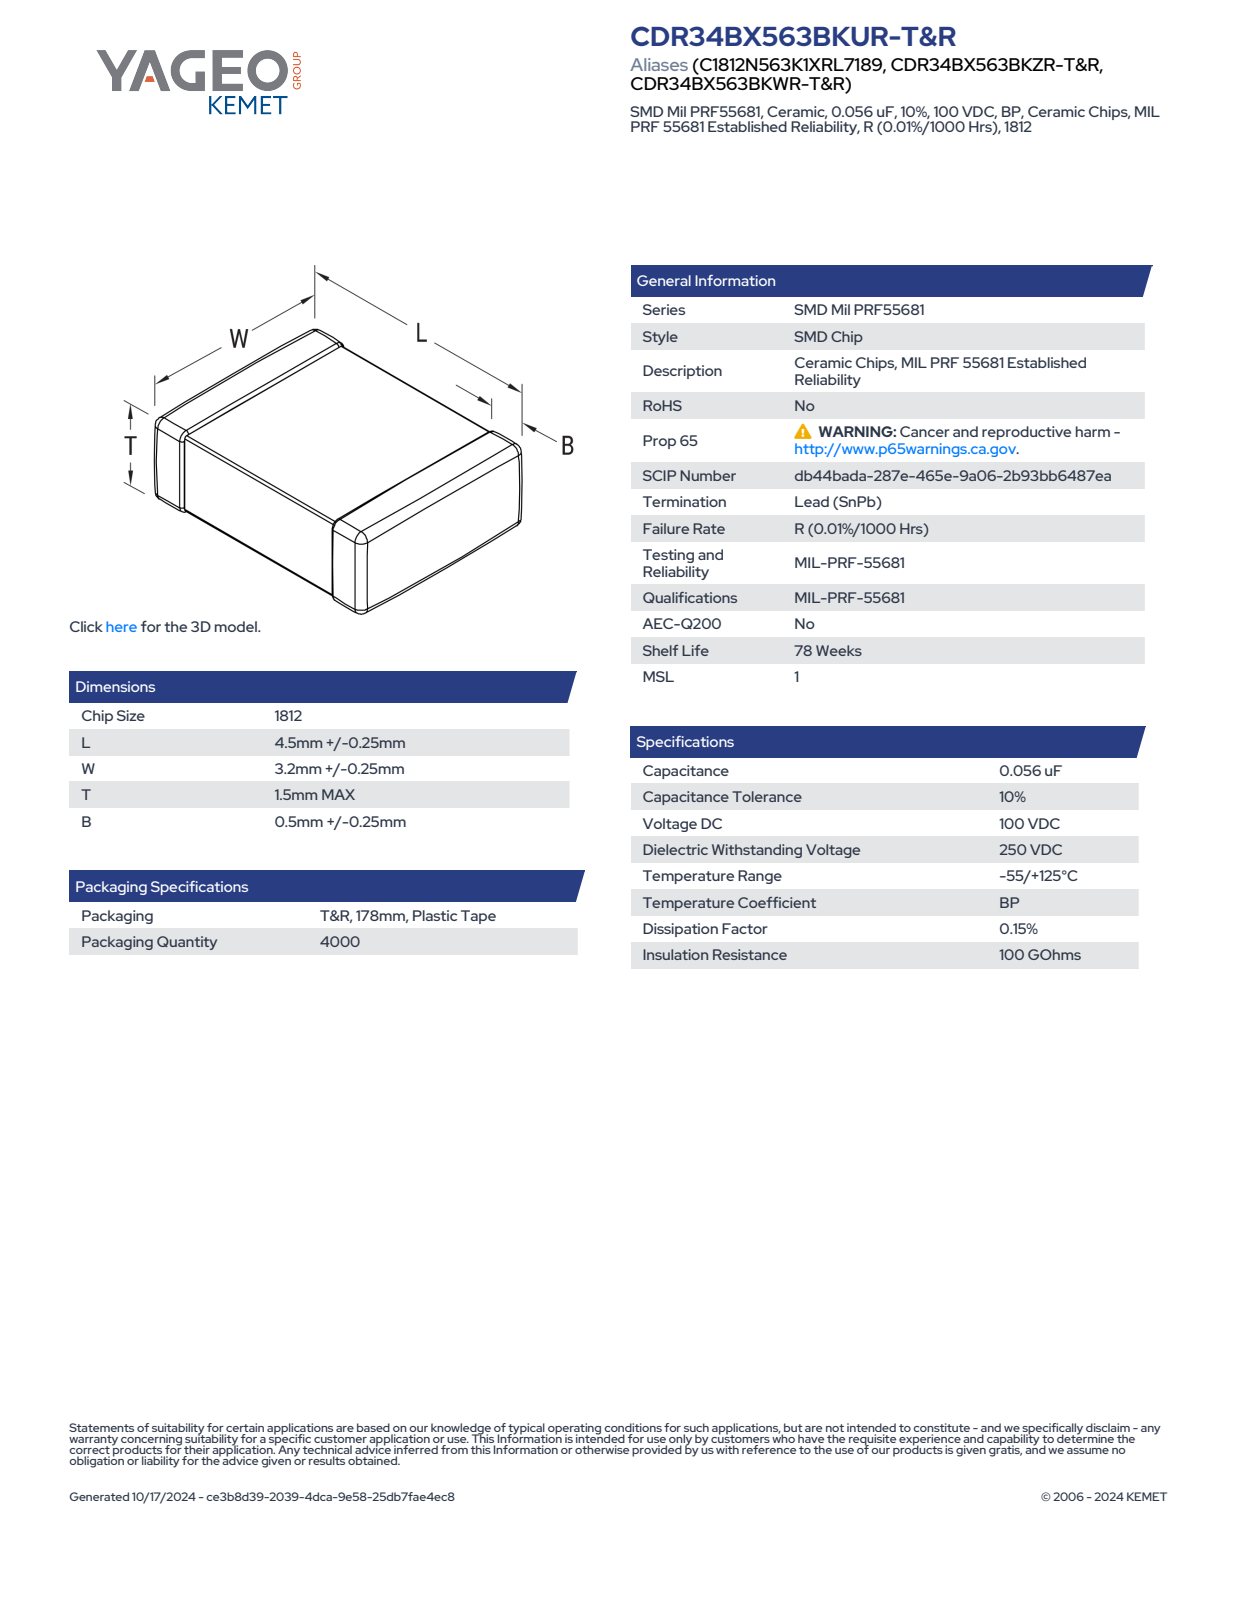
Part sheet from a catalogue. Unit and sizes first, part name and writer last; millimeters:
Units: millimetres
Overall size (bounding box): 4.75 × 3.45 × 1.5
Main face-to-face distances: 1.36, 1.43, 4.75, 1.5, 3.31, 3.38, 3.45, 1.47, 0.34, 1.91
Volume: 22 mm³ · Surface area: 56 mm²
Bodies: 4 solids, 125 faces (71 planar, 38 cylindrical, 16 other)
Part name (STEP PRODUCT): CCS_STDNOS_1812_L4.75W3.45T1.5B0.75
STEP written by: SolidWorks 2021 (AUTOMOTIVE_DESIGN)
